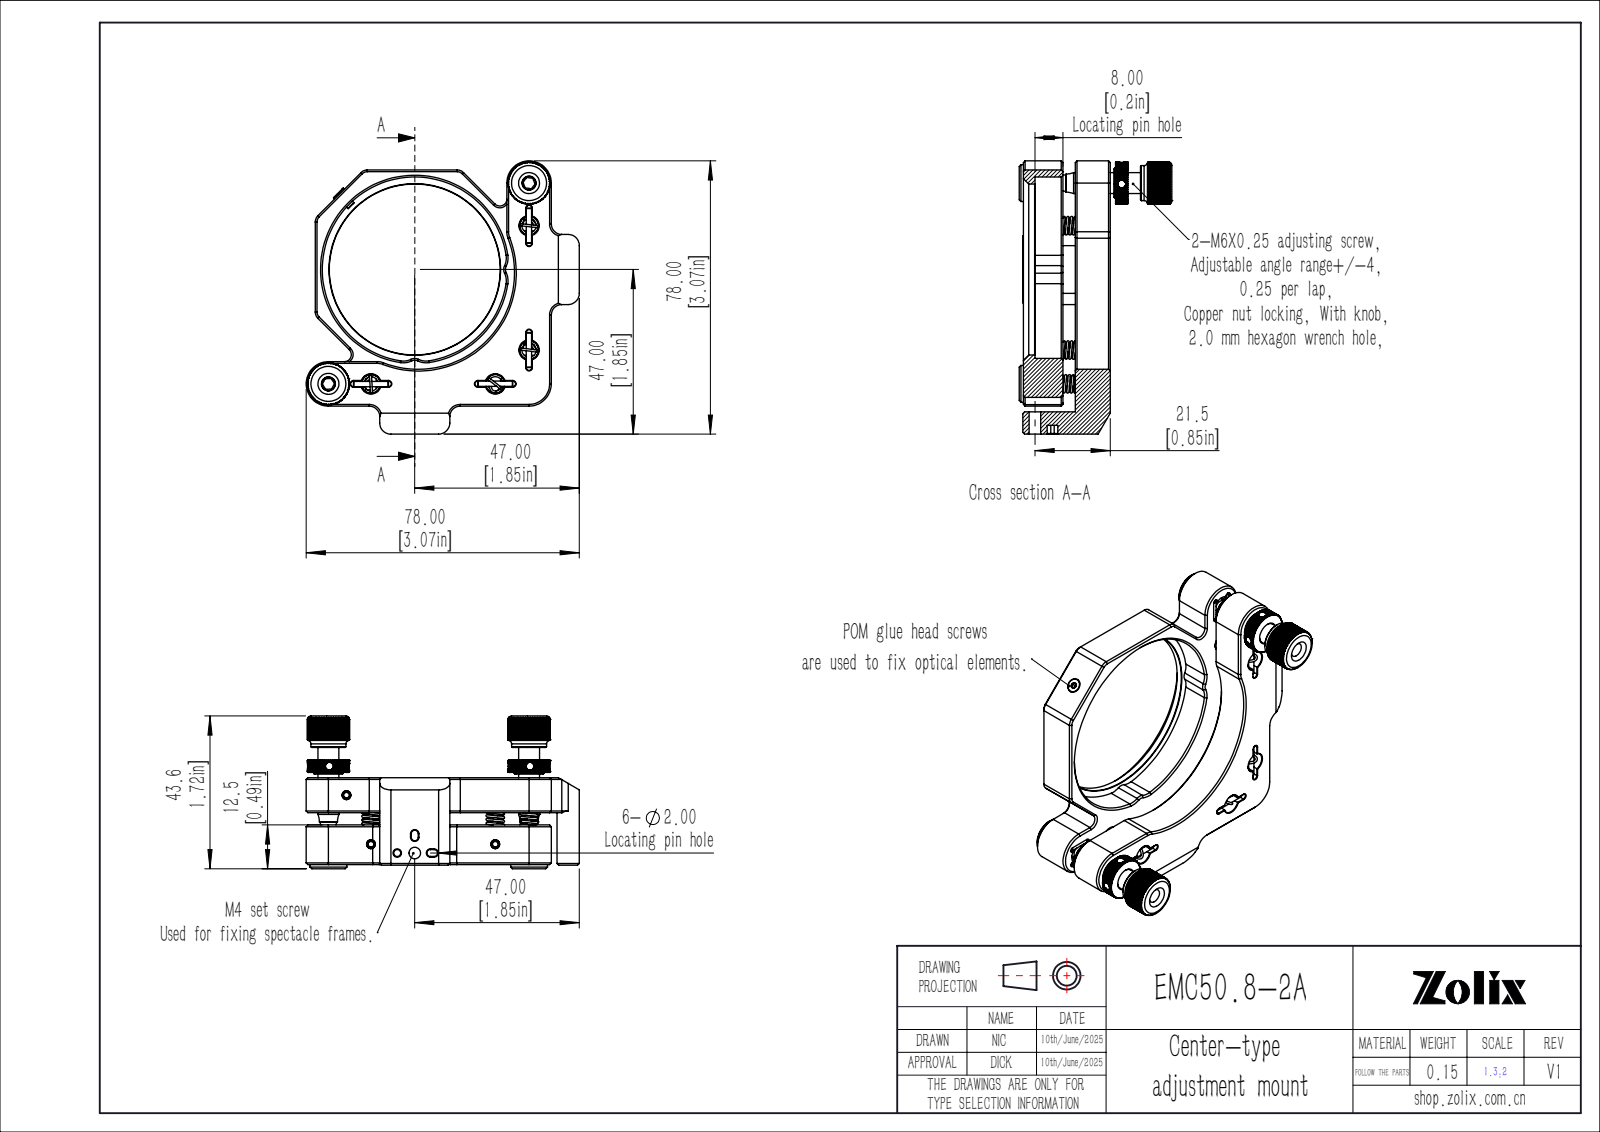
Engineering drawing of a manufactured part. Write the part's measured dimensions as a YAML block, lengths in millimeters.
part_name: "EMC50.8-2A"
step_written_by: "SolidWorks 2020 (CONFIG_CONTROL_DESIGN)"
units: millimeters
bodies: {solids: 0, faces: 1334, planar: 691, cylindrical: 405, other: 238}
overall_size: [78, 78, 43.62]
round_holes:
  - {diameter: 2.3, count: 8}
  - {diameter: 5.5, count: 4}
  - {diameter: 2, count: 3}
  - {diameter: 3.3, count: 3}
  - {diameter: 4, count: 2}
  - {diameter: 4.6, count: 2}
  - {diameter: 10, count: 2}
  - {diameter: 48.8, count: 1}
  - {diameter: 52.8, count: 1}
round_bosses_or_shafts:
  - {diameter: 1.5, count: 4}
  - {diameter: 10.5, count: 3}
  - {diameter: 8.5, count: 2}
  - {diameter: 6, count: 2}
  - {diameter: 4, count: 1}
  - {diameter: 2.4, count: 1}
partial_cylinders:
  - {radius: 0.8, count: 16}
  - {radius: 5, count: 10}
  - {radius: 1, count: 8}
  - {radius: 2.5, count: 6}
  - {radius: 3, count: 4}
  - {radius: 3.17, count: 4}
  - {radius: 0.75, count: 3}
  - {radius: 6.35, count: 3}
face_to_face_distances: [3.5, 11.32, 13.5, 24.82, 14.82, 10, 8, 11.5, 67.4, 75.4]
hole_center_spacings: [60.2, 46.17, 5, 9.65, 12.15, 34.96, 35.5, 39.94]
